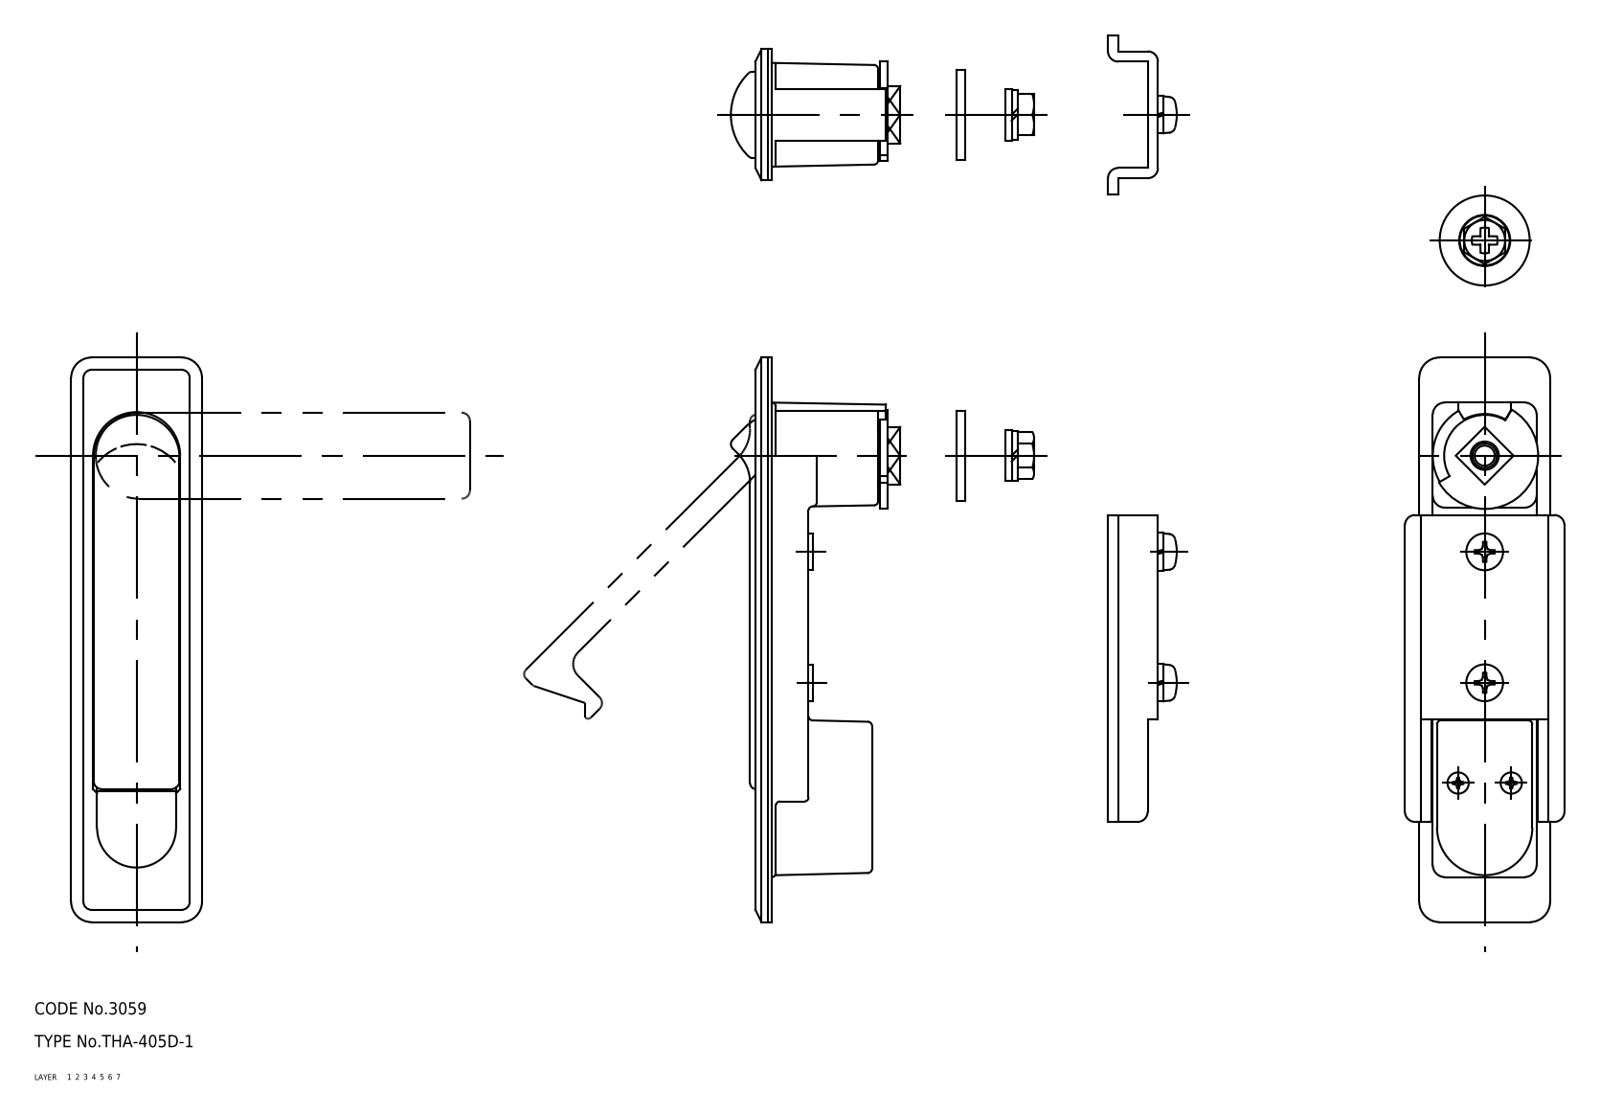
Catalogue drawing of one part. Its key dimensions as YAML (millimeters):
part_name: "screw; bracket; lock; washer (+7 more)"
step_written_by: "CADfix (AUTOMOTIVE_DESIGN)"
units: millimeters
bodies: {solids: 11, faces: 483, planar: 0, cylindrical: 0, other: 483}
overall_size: [138, 48.5, 39]
volume: 57160
surface_area: 45834
